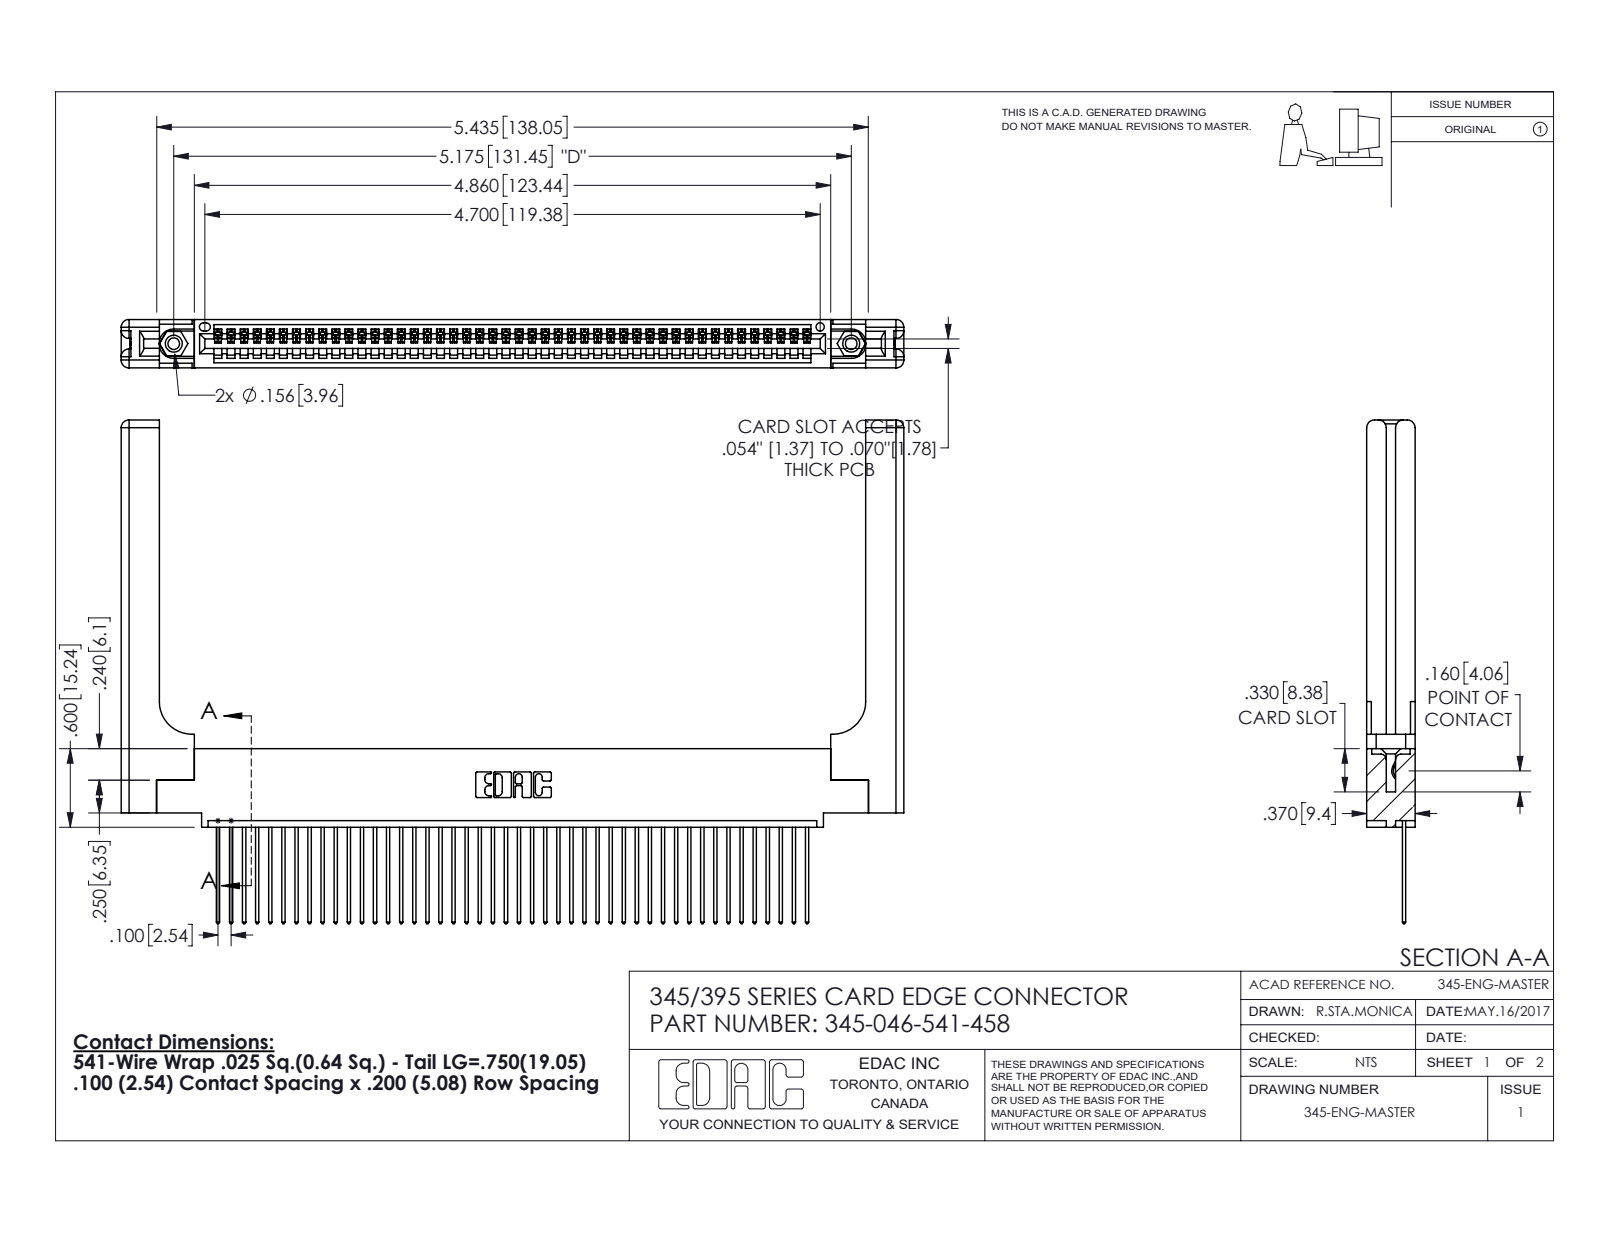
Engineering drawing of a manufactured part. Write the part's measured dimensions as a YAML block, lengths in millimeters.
part_name: "345-220-058_345-220-058; 345-250-001_345-250-001-102; 345-292-001_345-293-141; 345-046-541-458 (+1 more)"
step_written_by: "SolidWorks 2016 (CONFIG_CONTROL_DESIGN)"
units: millimeters
bodies: {solids: 51, faces: 3054, planar: 2072, cylindrical: 922, other: 60}
overall_size: [151.9, 97.7, 9.4]
volume: 23040
surface_area: 25650
round_holes:
  - {diameter: 2.3, count: 2}
  - {diameter: 3.2, count: 2}
  - {diameter: 4, count: 2}
  - {diameter: 1.6, count: 1}
round_bosses_or_shafts:
  - {diameter: 3.9, count: 2}
partial_cylinders:
  - {radius: 0.2, count: 92}
  - {radius: 0.3, count: 92}
  - {radius: 0.3, count: 22}
  - {radius: 1.5, count: 16}
  - {radius: 0.2, count: 6}
  - {radius: 0.8, count: 6}
  - {radius: 0.7, count: 3}
  - {radius: 0.8, count: 2}
face_to_face_distances: [1.8, 7.6, 9.4, 2.5, 6.9, 0.6, 5.1, 5.7, 3.8, 3.8]
hole_center_spacings: [6.9, 125.5, 131.4]
